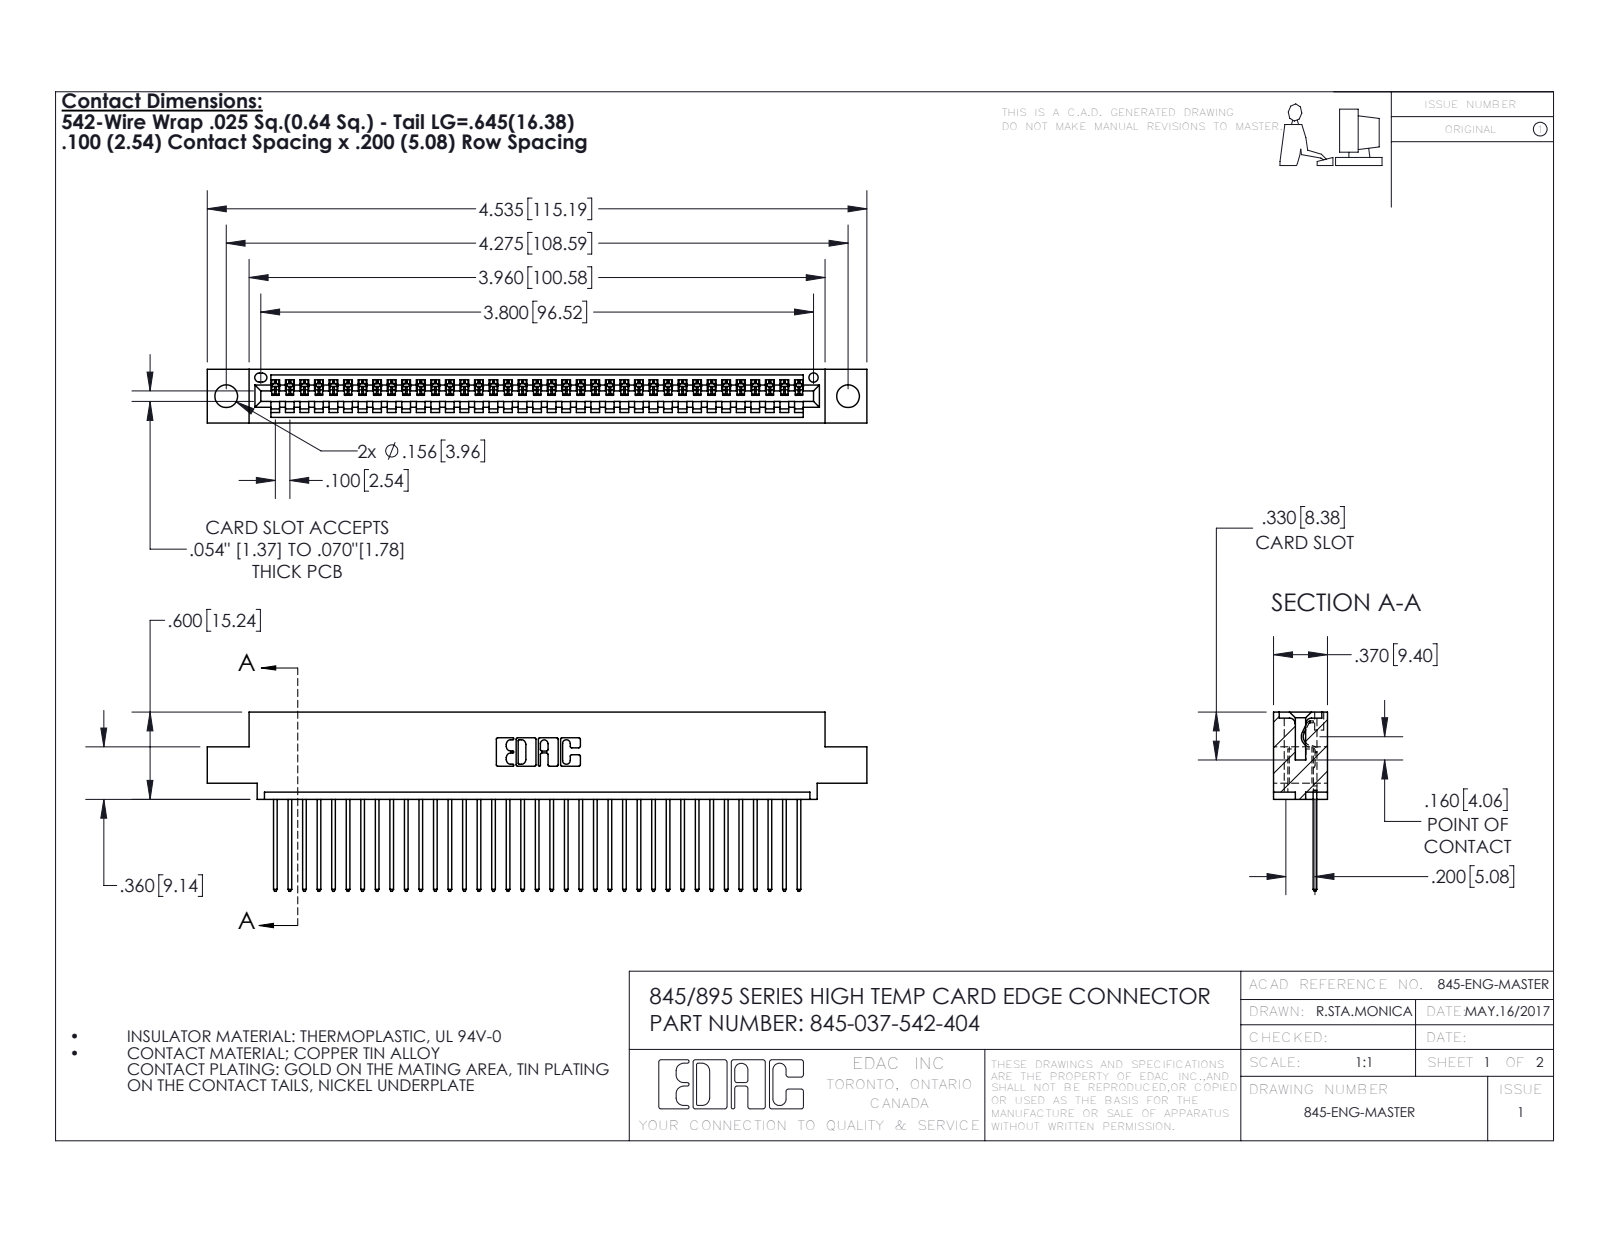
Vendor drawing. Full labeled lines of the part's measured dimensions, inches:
Part name (STEP PRODUCT): 345-292-001_345-293-142; 345 Part_0.110 Offset - 0.156 Dia-TH; 345-037-542-404
STEP written by: SolidWorks 2016 (CONFIG_CONTROL_DESIGN)
Units: inches
Bodies: 38 solids, 2276 faces (1564 planar, 712 cylindrical, 0 other)
Overall size (bounding box): 4.535 × 1.232 × 0.37
Volume: 0.66 in³ · Surface area: 22.82 in²
Round holes (diameter × count): ⌀0.156 ×2, ⌀0.064 ×1
Partial cylindrical surfaces — rounded edges, fillets, slot ends (radius × count): R0.006 ×74, R0.01 ×74, R0.01 ×22, R0.007 ×6, R0.031 ×6, R0.026 ×3, R0.031 ×2, R0.04 ×2
Main face-to-face distances: 0.072, 0.298, 0.37, 0.098, 0.272, 0.025, 0.2, 0.225, 0.149, 0.072
Hole centre spacings: 0.27, 4.039, 4.275
